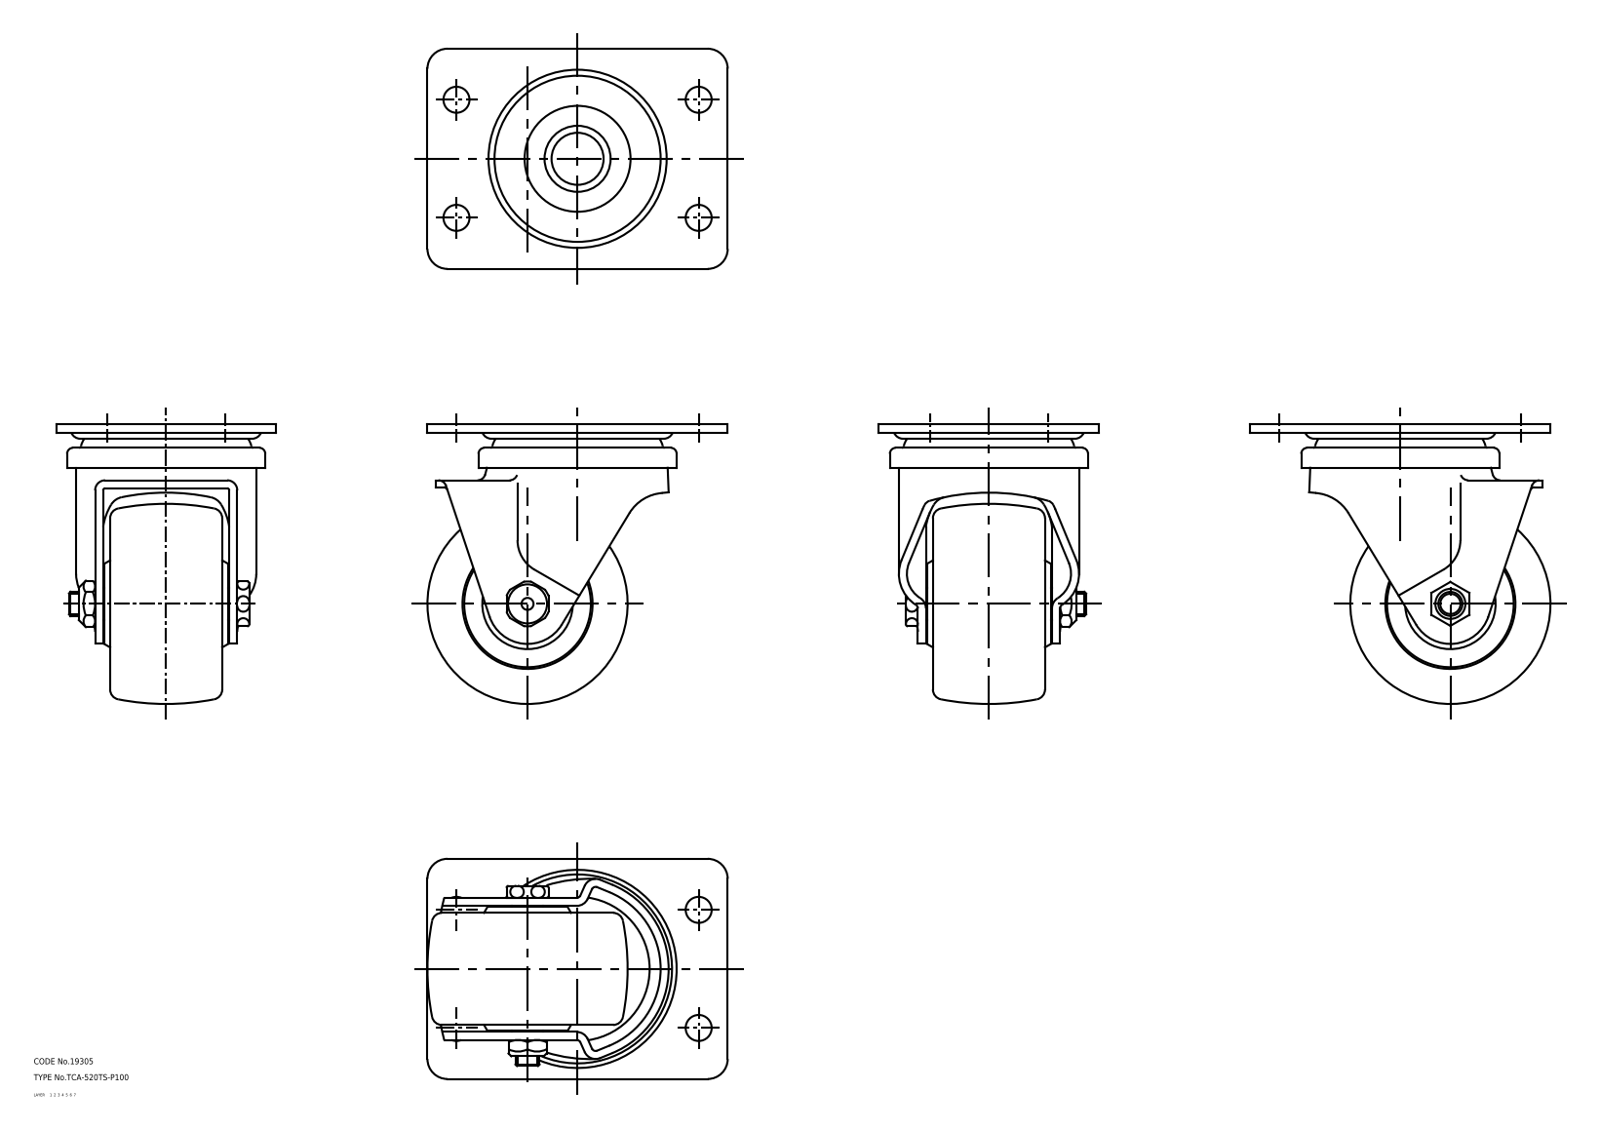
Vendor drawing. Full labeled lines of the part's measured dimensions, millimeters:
Part name (STEP PRODUCT): 67126330; 67126343; 67126356; 67126369 (+1 more)
STEP written by: CADfix (AUTOMOTIVE_DESIGN)
Units: millimetres
Bodies: 5 solids, 211 faces (0 planar, 0 cylindrical, 211 other)
Overall size (bounding box): 150 × 140 × 110
Volume: 681 340 mm³ · Surface area: 139 182 mm²
